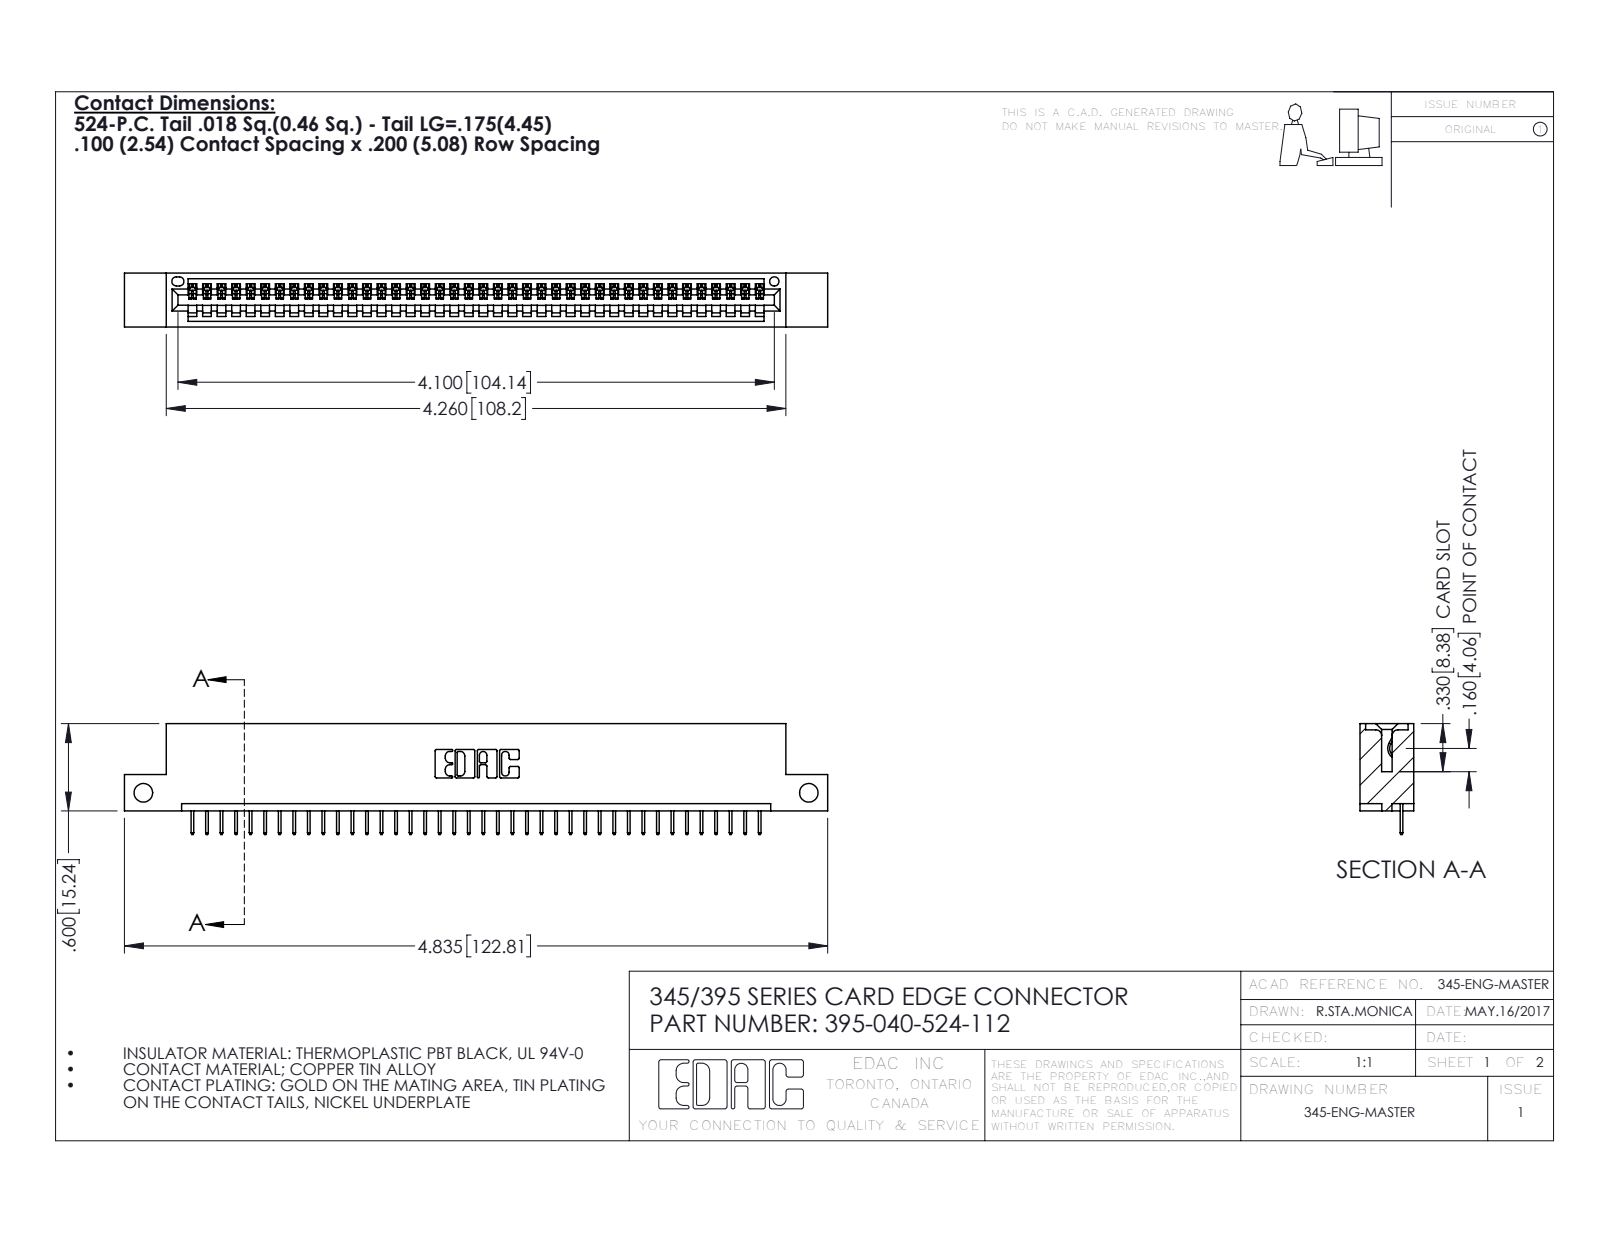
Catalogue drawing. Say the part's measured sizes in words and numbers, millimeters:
The part is named "345 Part_Flush Mounting Lugs - Side Mount; 395-040-524-112; 345-292-001_345-293-124". Its 3-D file was written by "SolidWorks 2016 (CONFIG_CONTROL_DESIGN)". It is 41 solids with 2606 faces: 1920 planar, 686 cylindrical and 0 other. Overall it measures 122.8 by 19.4 by 9.4 millimeters. Its volume is 11 400 cubic millimeters and its surface area 14 480 square millimeters. Round holes: 2 of diameter 3.3, 1 of diameter 1.6. Partial cylindrical surfaces (rounded edges, fillets, slot ends): 80 of radius 0.2, 22 of radius 0.3, 6 of radius 0.2, 6 of radius 0.8, 3 of radius 0.7, 2 of radius 0.8, 2 of radius 1, 1 of radius 0.4. The main face-to-face distances are 7.6, 1.8, 9.4, 5.1, 2.5, 6.9, 0.6, 5.7, 1.8, 3.8. The hole center spacings are 116.2.
